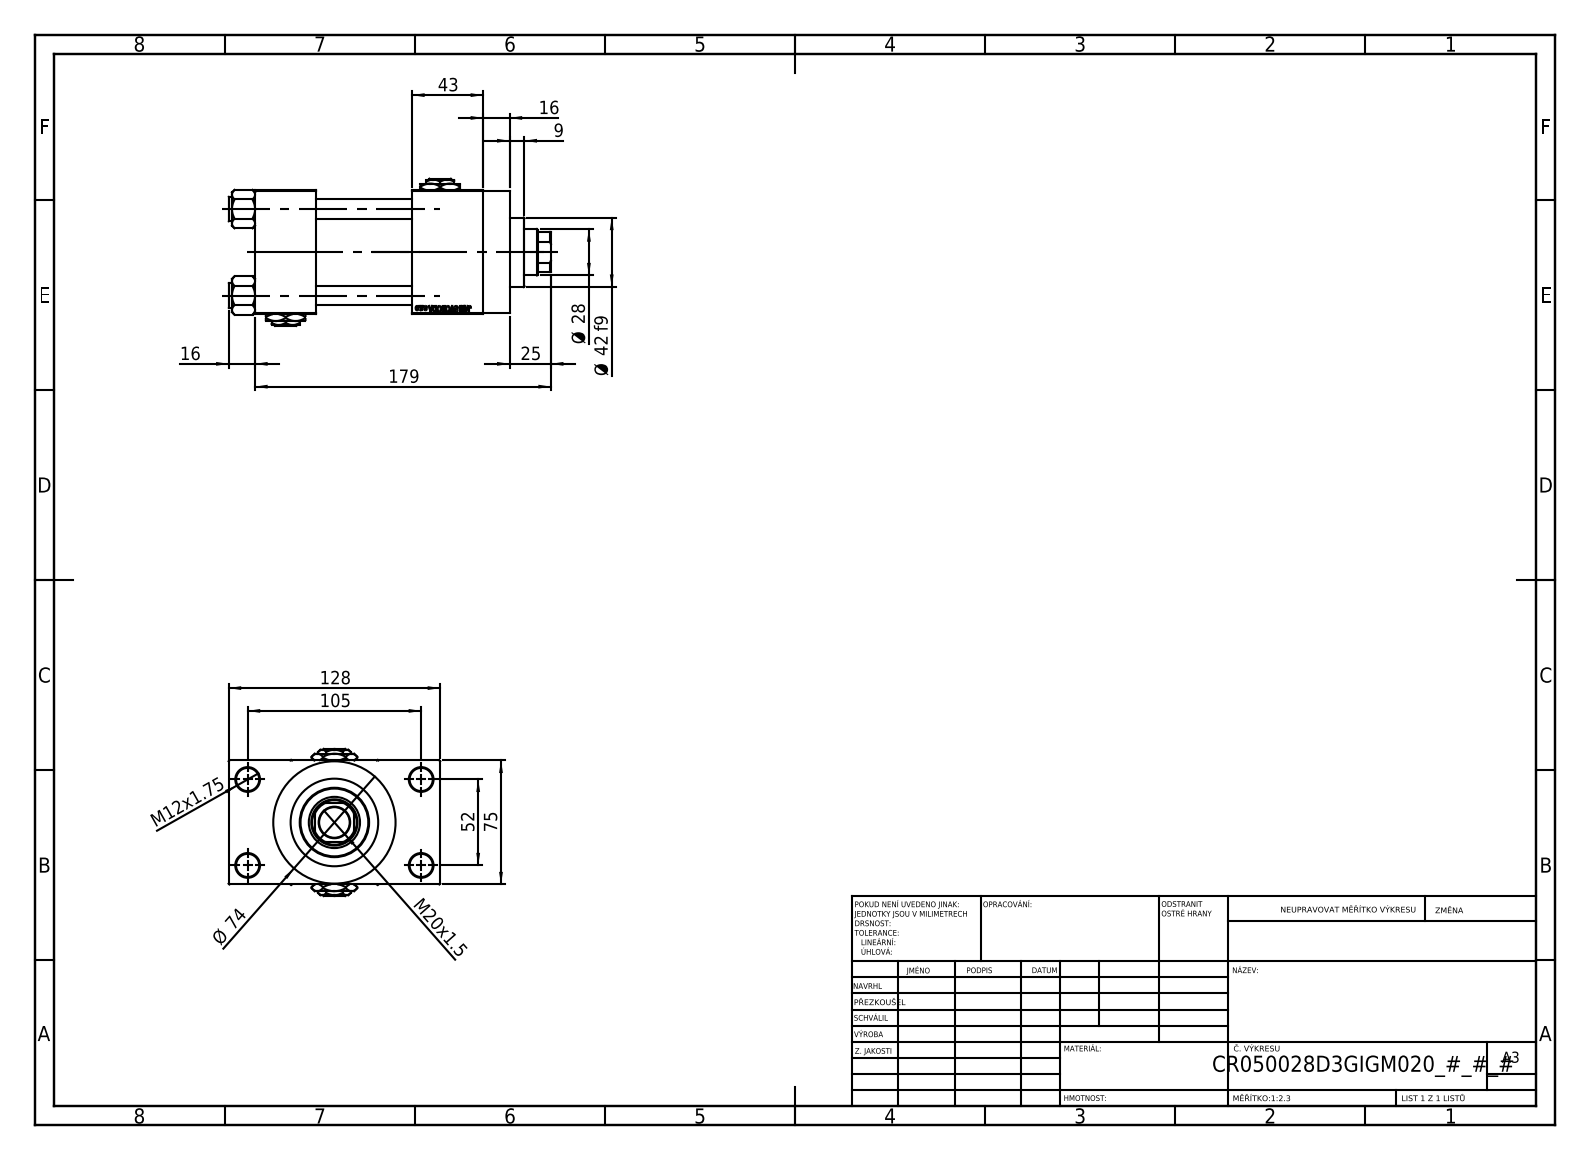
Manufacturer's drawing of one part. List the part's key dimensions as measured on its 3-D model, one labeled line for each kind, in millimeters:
Part name (STEP PRODUCT): NUT_M5_D; V215CR_D_TYCINKA; Zatka_pro_OIL_PORT; V215CR_VCP_D (+2 more)
STEP written by: SolidWorks 2019 (CONFIG_CONTROL_DESIGN)
Units: millimetres
Bodies: 13 solids, 1198 faces (543 planar, 95 cylindrical, 560 other)
Overall size (bounding box): 195 × 128 × 89
Volume: 816 319 mm³ · Surface area: 172 820 mm²
Round holes (diameter × count): ⌀12 ×4, ⌀14 ×4, ⌀7 ×3, ⌀20.96 ×3, ⌀30 ×3, ⌀18.5 ×1, ⌀28 ×1, ⌀31 ×1, ⌀41 ×1, ⌀50 ×1, ⌀53 ×1
Round bosses / shafts (diameter × count): ⌀15 ×4, ⌀74 ×1, ⌀56 ×1, ⌀42 ×1
Partial cylindrical surfaces — rounded edges, fillets, slot ends (radius × count): R13.5 ×1
Main face-to-face distances: 75, 58, 37, 95, 101.5, 26.5, 138, 101, 43, 16
Hole centre spacings: 26.35, 36.98, 52.3, 58.43, 58.59, 78.65, 94.37, 52
